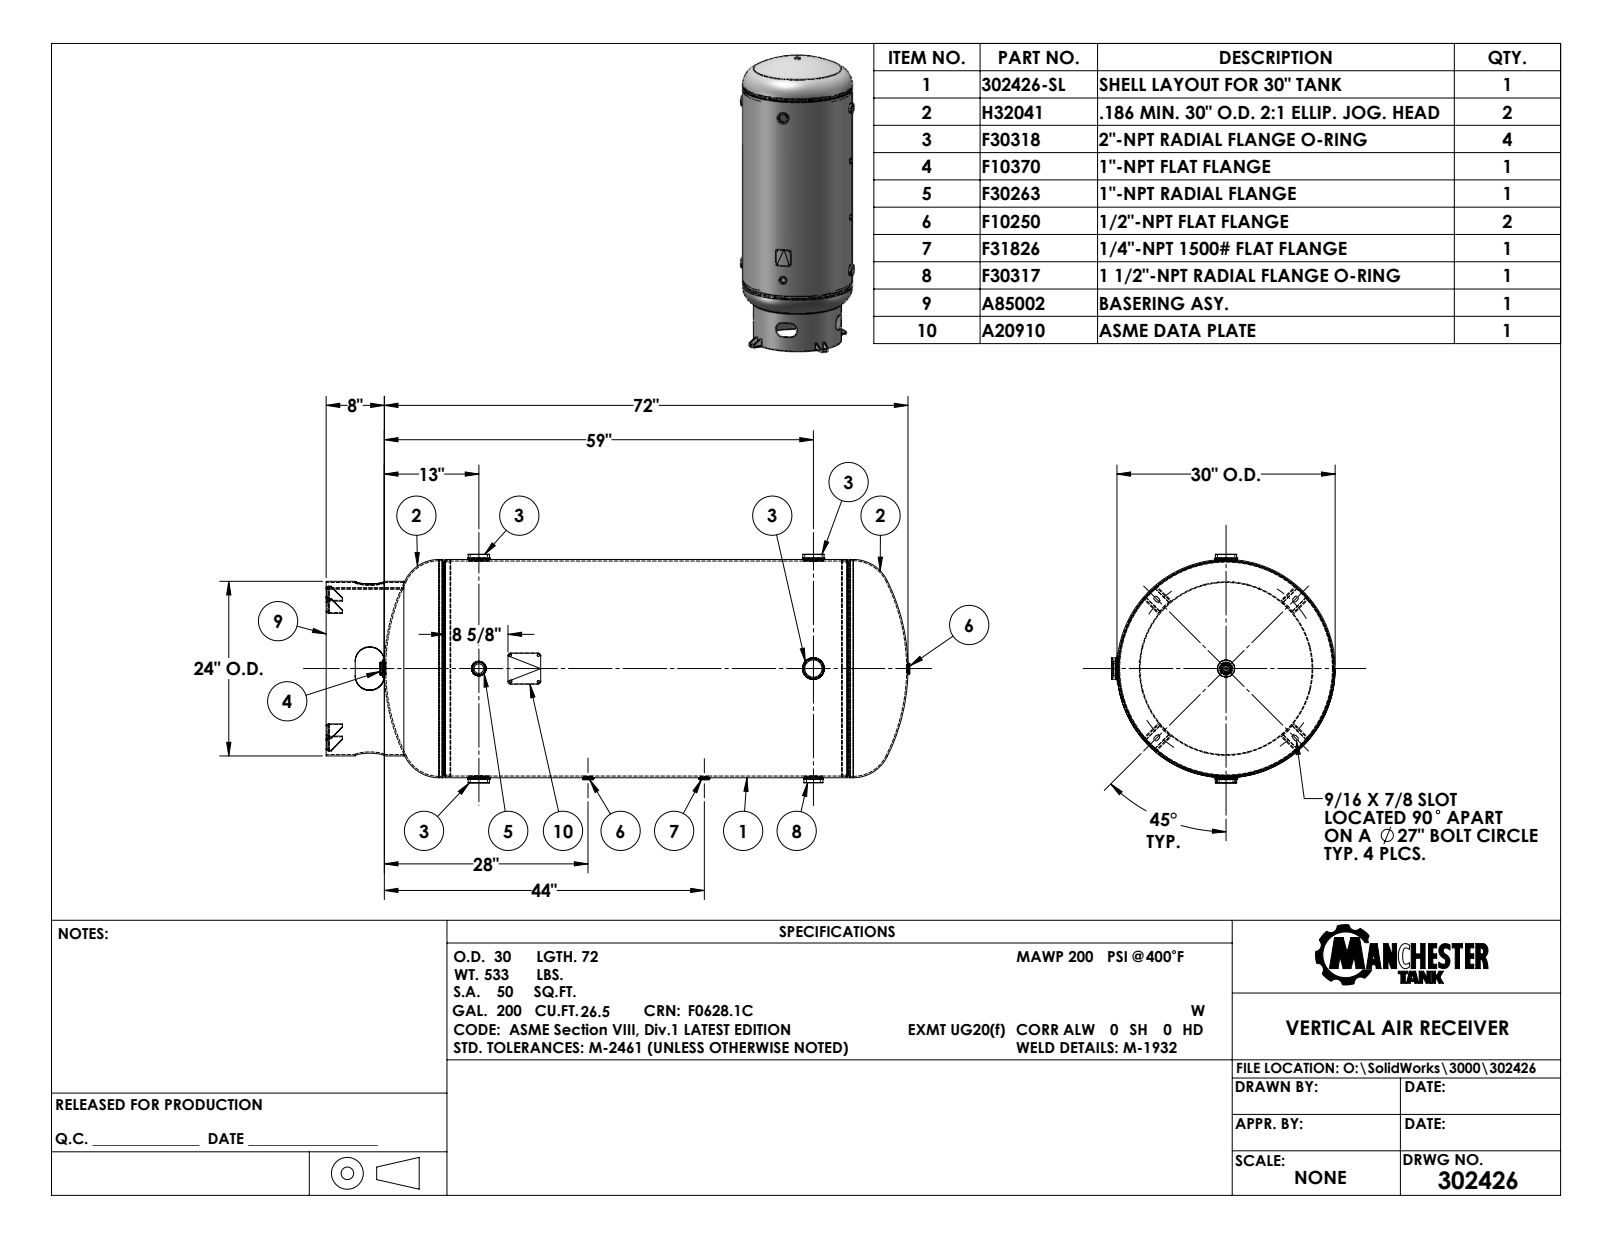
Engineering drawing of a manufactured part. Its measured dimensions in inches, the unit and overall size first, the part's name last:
Units: inches
Overall size (bounding box): 80.272 × 31.412 × 30.706
Round holes (diameter × count): ⌀2.375 ×3, ⌀0.84 ×2, ⌀0.54 ×1, ⌀1.315 ×1, ⌀1.315 ×1, ⌀1.9 ×1, ⌀23.656 ×1, ⌀29.256 ×1, ⌀29.546 ×1, ⌀29.628 ×1
Round bosses / shafts (diameter × count): ⌀3 ×3, ⌀2.625 ×3, ⌀1.45 ×3, ⌀1.438 ×3, ⌀1.062 ×2, ⌀30 ×1, ⌀29.63 ×1, ⌀24 ×1
Partial cylindrical surfaces — rounded edges, fillets, slot ends (radius × count): R0.25 ×8, R0.281 ×8, R0.384 ×8, R10 ×3, R7 ×1, R7.5 ×1, R15.06 ×1
Main face-to-face distances: 0.134, 0.75, 54.5, 2.383, 71.625, 16.375, 55.25, 16.241, 71.491, 70.875
Hole centre spacings: 15, 31, 46, 16
Volume: 1 733 in³ · Surface area: 16 691 in²
Bodies: 19 solids, 452 faces (142 planar, 130 cylindrical, 180 other)
Part name (STEP PRODUCT): 302426 STEP FILE
STEP written by: SolidWorks 2020 (AUTOMOTIVE_DESIGN)
